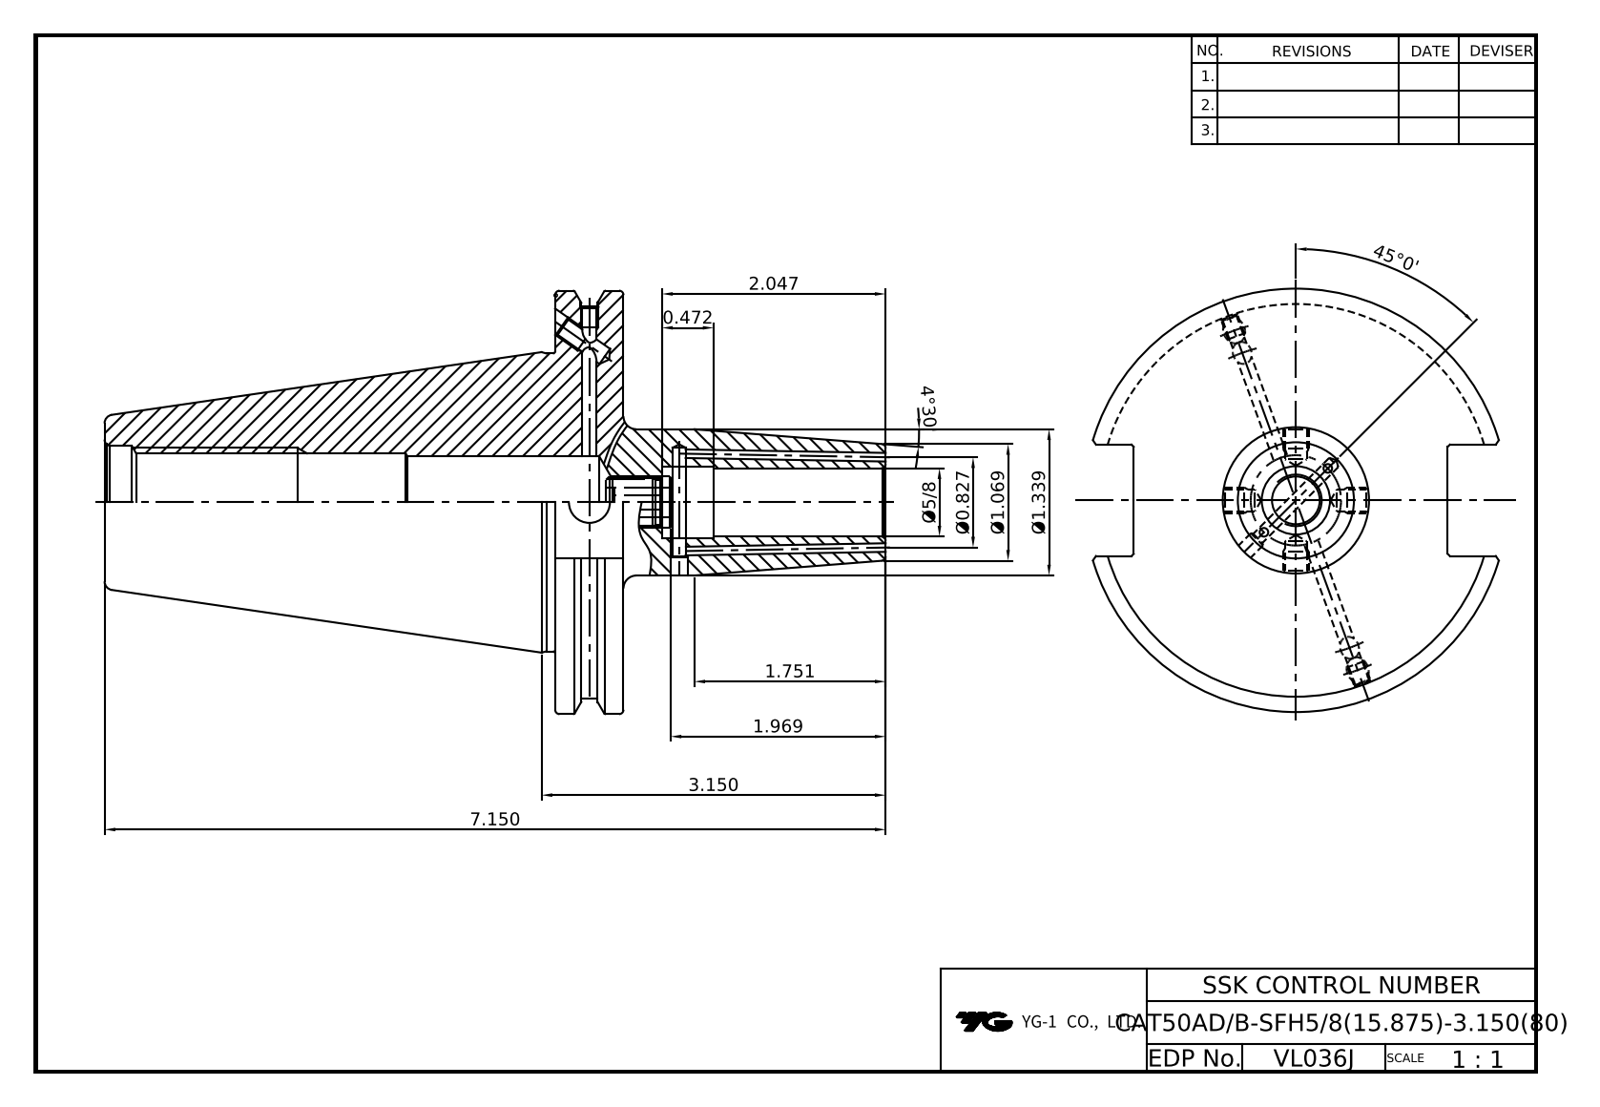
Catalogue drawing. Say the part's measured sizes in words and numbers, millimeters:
The part is named "LO-CAT50ADB-SFH15.875C-80". Its 3-D file was written by "Autodesk Inventor 2025 (AUTOMOTIVE_DESIGN)". It is 1 solid with 88 faces: 37 planar, 28 cylindrical and 23 other. Overall it measures 181.6 by 98.42 by 94.69 millimeters. Its volume is 355 041 cubic millimeters and its surface area 54 223 square millimeters. Round holes: 2 of diameter 2.5, 2 of diameter 3.24, 2 of diameter 4.13, 2 of diameter 4.2, 2 of diameter 5, 1 of diameter 9.53, 1 of diameter 10.92, 1 of diameter 15.87, 1 of diameter 16.47, 1 of diameter 21.97, 1 of diameter 26.2. Round bosses or shafts: 1 of diameter 98.42, 1 of diameter 91.29, 1 of diameter 69.25, 1 of diameter 34. The main face-to-face distances are 15.88, 104.77, 120.65, 73.03, 25.9, 181.6, 76.83, 60.95, 110.82, 6.05.
